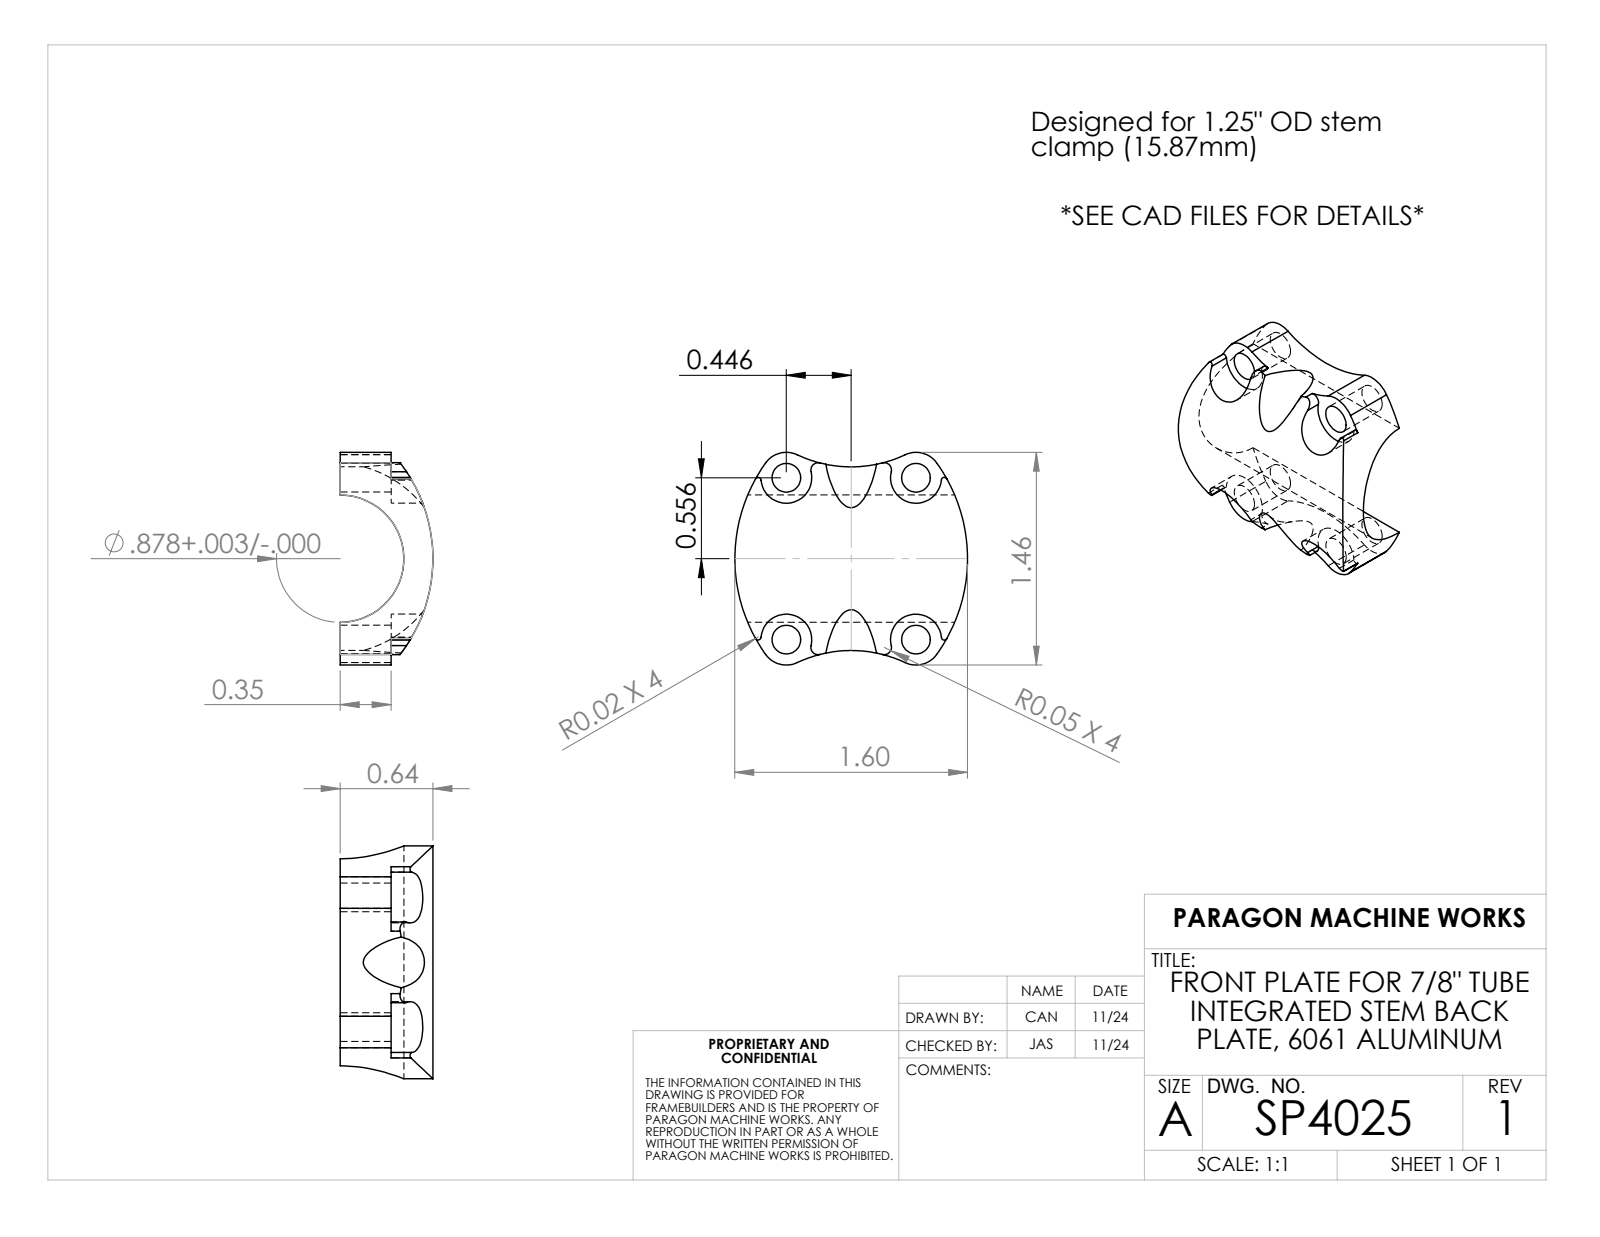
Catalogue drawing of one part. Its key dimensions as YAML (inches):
part_name: "SP4025_V2"
step_written_by: "SolidWorks 2023 (AUTOMOTIVE_DESIGN)"
units: inches
bodies: {solids: 1, faces: 47, planar: 6, cylindrical: 37, other: 4}
overall_size: [1.6, 1.462, 0.638]
volume: 0.548
surface_area: 7.725
round_holes:
  - {diameter: 0.197, count: 4}
partial_cylinders:
  - {radius: 0.02, count: 4}
  - {radius: 0.05, count: 4}
  - {radius: 0.175, count: 4}
  - {radius: 0.868, count: 2}
  - {radius: 1.126, count: 2}
  - {radius: 0.437, count: 1}
  - {radius: 1.073, count: 1}
face_to_face_distances: [0.35]
hole_center_spacings: [0.891, 1.112, 1.425]
